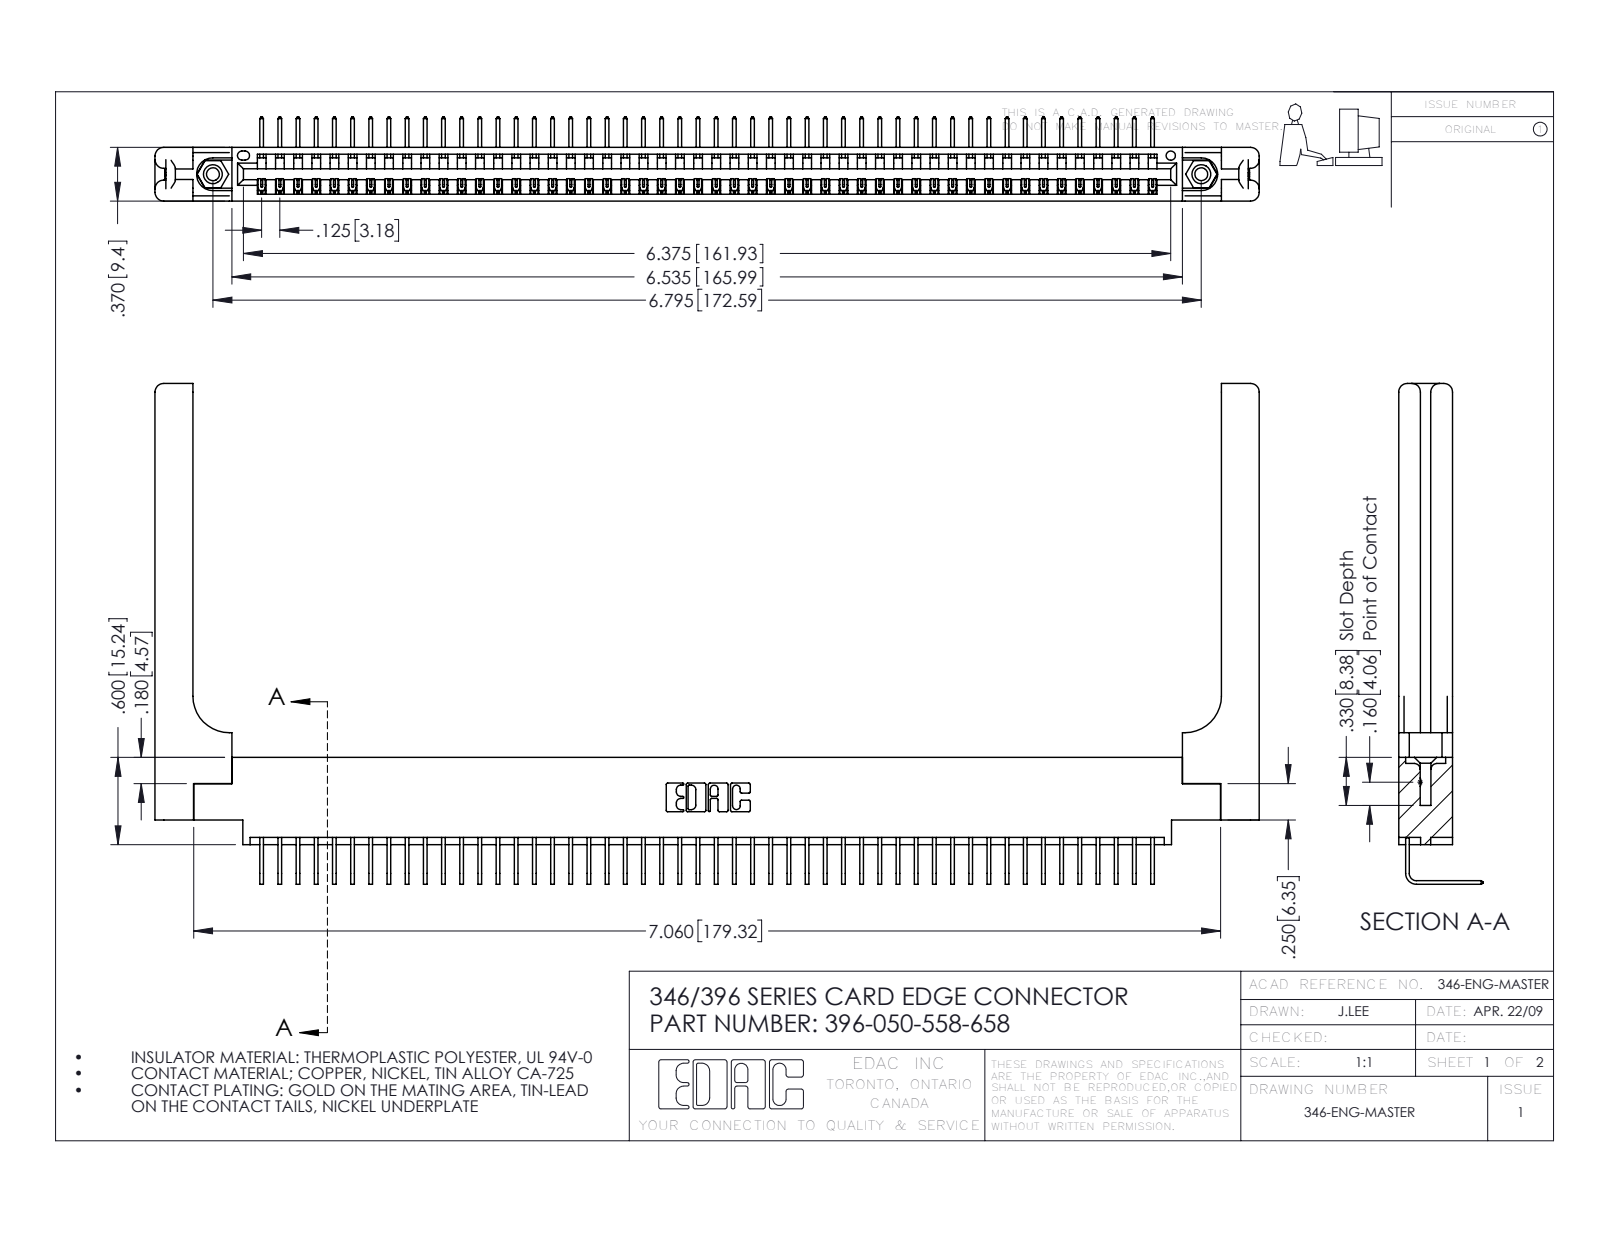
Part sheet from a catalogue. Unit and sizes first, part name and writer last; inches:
Units: inches
Overall size (bounding box): 7.591 × 3.443 × 0.58
Round holes (diameter × count): ⌀0.089 ×2, ⌀0.125 ×2, ⌀0.156 ×2, ⌀0.064 ×1
Round bosses / shafts (diameter × count): ⌀0.155 ×2
Partial cylindrical surfaces — rounded edges, fillets, slot ends (radius × count): R0.006 ×100, R0.01 ×22, R0.06 ×16, R0.007 ×6, R0.031 ×6, R0.026 ×3, R0.03 ×2, R0.031 ×2
Main face-to-face distances: 0.37, 0.322, 0.048, 0.072, 0.148, 0.025, 0.15, 0.298, 0.25, 0.222
Hole centre spacings: 0.246, 6.586, 6.795
Volume: 1.589 in³ · Surface area: 45.82 in²
Bodies: 55 solids, 3382 faces (2328 planar, 994 cylindrical, 60 other)
Part name (STEP PRODUCT): 396-050-558-658; 345-250-001_345-250-001-102; 346-220-058_345-220-058; 345-292-001_558 Tail - 2 (+1 more)
STEP written by: SolidWorks 2016 (CONFIG_CONTROL_DESIGN)
